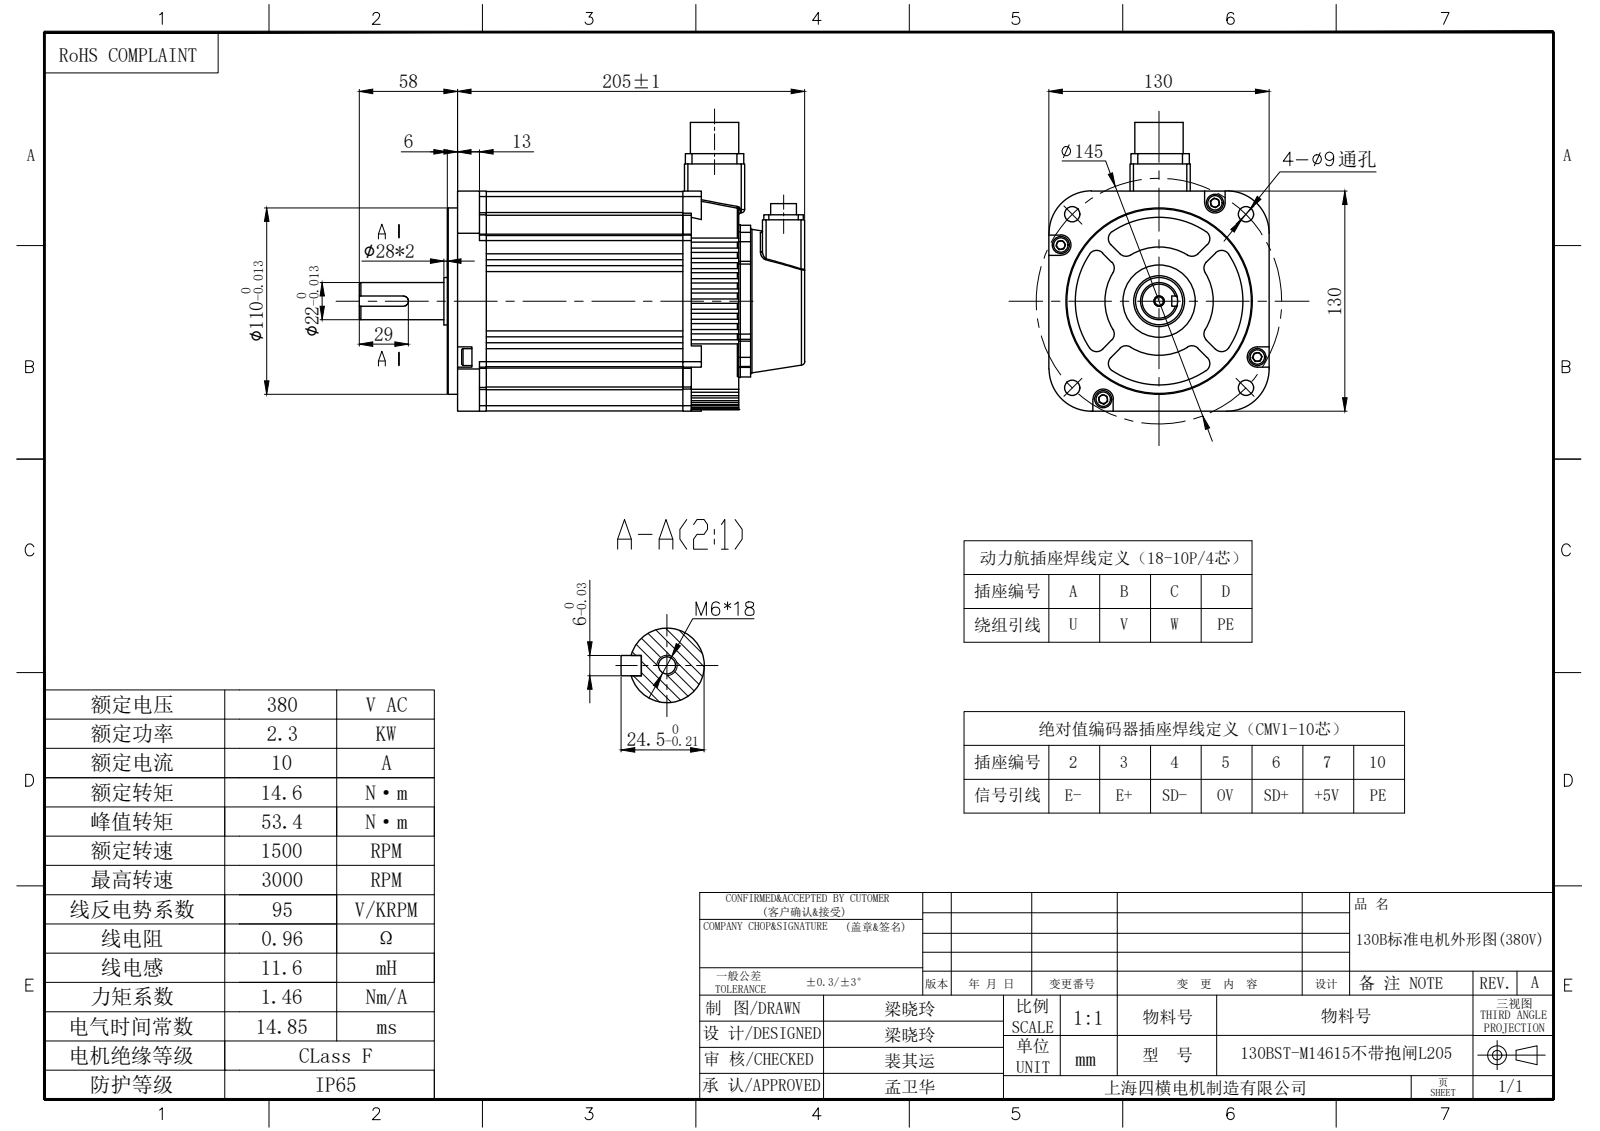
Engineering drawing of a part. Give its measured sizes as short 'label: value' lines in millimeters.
name: 130BST后端盖02; hexagon socket head cap screws gb_ M6; 130BST后盖; 130BST-M14615不带抱闸L205 (+2 more)
written by: SolidWorks 2020 (AUTOMOTIVE_DESIGN)
unit: mm
bodies: 44 solids, 798 faces (387 planar, 332 cylindrical, 79 other)
size: 263 × 170.5 × 130
volume: 2 626 000 mm³; area: 244 692 mm²
holes: 8× ⌀3, 8× ⌀6.6, 5× ⌀5, 4× ⌀9, 1× ⌀11.5, 1× ⌀24, 1× ⌀42.6
bosses: 4× ⌀10, 4× ⌀6, 4× ⌀2.5, 1× ⌀110, 1× ⌀30, 1× ⌀28.5, 1× ⌀28, 1× ⌀22
rounds: 16× R1.5, 16× R3.25, 16× R5, 15× R2, 13× R3, 8× R3.5, 4× R2.25, 4× R2.5
face distances: 116, 149, 33, 133, 129.5, 17, 166, 26, 3.5, 103.5
hole spacings: 1.34, 12.02, 17, 27, 47.91, 66.73, 68, 94.37
